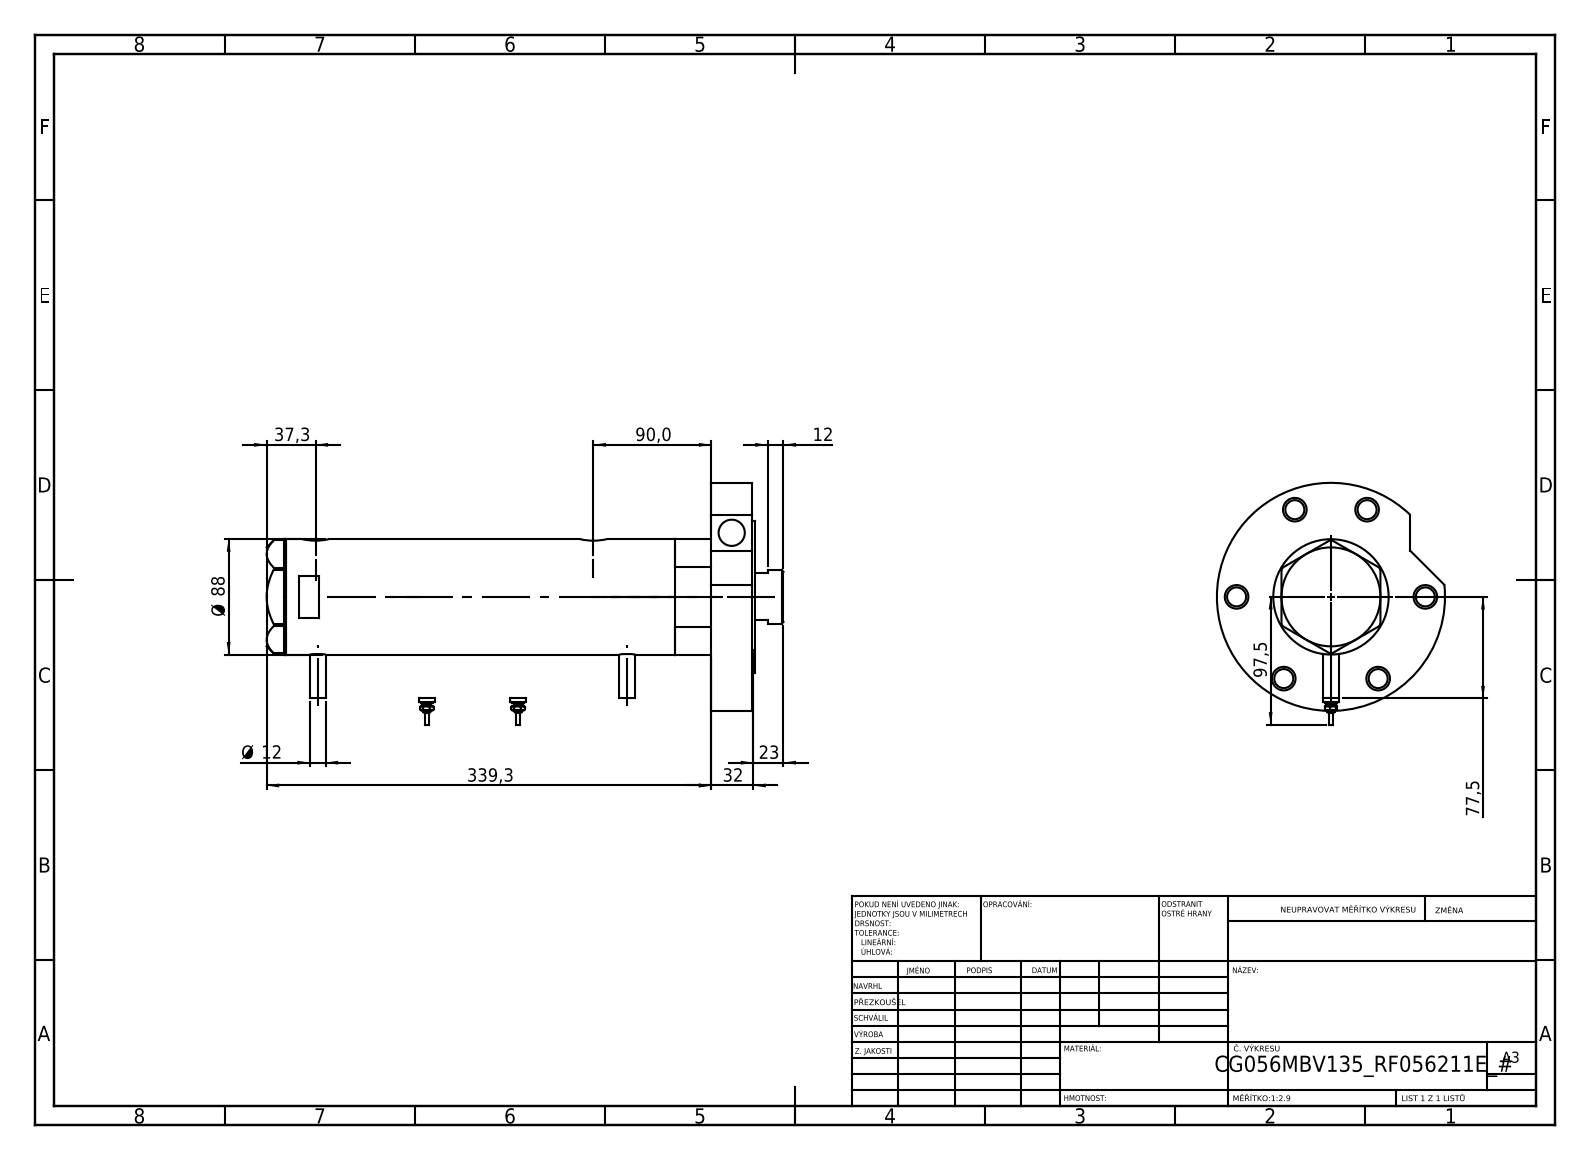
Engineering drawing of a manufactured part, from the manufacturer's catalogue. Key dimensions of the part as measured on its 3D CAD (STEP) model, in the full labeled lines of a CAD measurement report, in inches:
Part name (STEP PRODUCT): V270CG_FRONT; Switch; V270CG_VC; V270CG_MIDDLE (+2 more)
STEP written by: SolidWorks 2019 (CONFIG_CONTROL_DESIGN)
Units: inches
Bodies: 7 solids, 257 faces (91 planar, 102 cylindrical, 64 other)
Overall size (bounding box): 15.524 × 7.264 × 6.85
Volume: 157.3 in³ · Surface area: 560.1 in²
Round holes (diameter × count): ⌀0.571 ×7, ⌀0.709 ×6, ⌀0.787 ×3, ⌀0.492 ×2, ⌀0.518 ×2, ⌀1.654 ×1, ⌀1.713 ×1, ⌀2.205 ×1, ⌀2.362 ×1, ⌀2.953 ×1, ⌀3.15 ×1
Round bosses / shafts (diameter × count): ⌀0.472 ×4, ⌀0.354 ×2, ⌀0.276 ×2, ⌀0.177 ×2, ⌀0.098 ×2, ⌀6.85 ×1, ⌀4.567 ×1, ⌀3.465 ×1
Main face-to-face distances: 1.22, 0.079, 14.067, 12.768, 13.988, 1.299, 9.228, 3.539, 4.76, 4.839
Hole centre spacings: 2.835, 3.15, 4.714, 4.91, 5.085, 5.657, 0.067, 1.016
